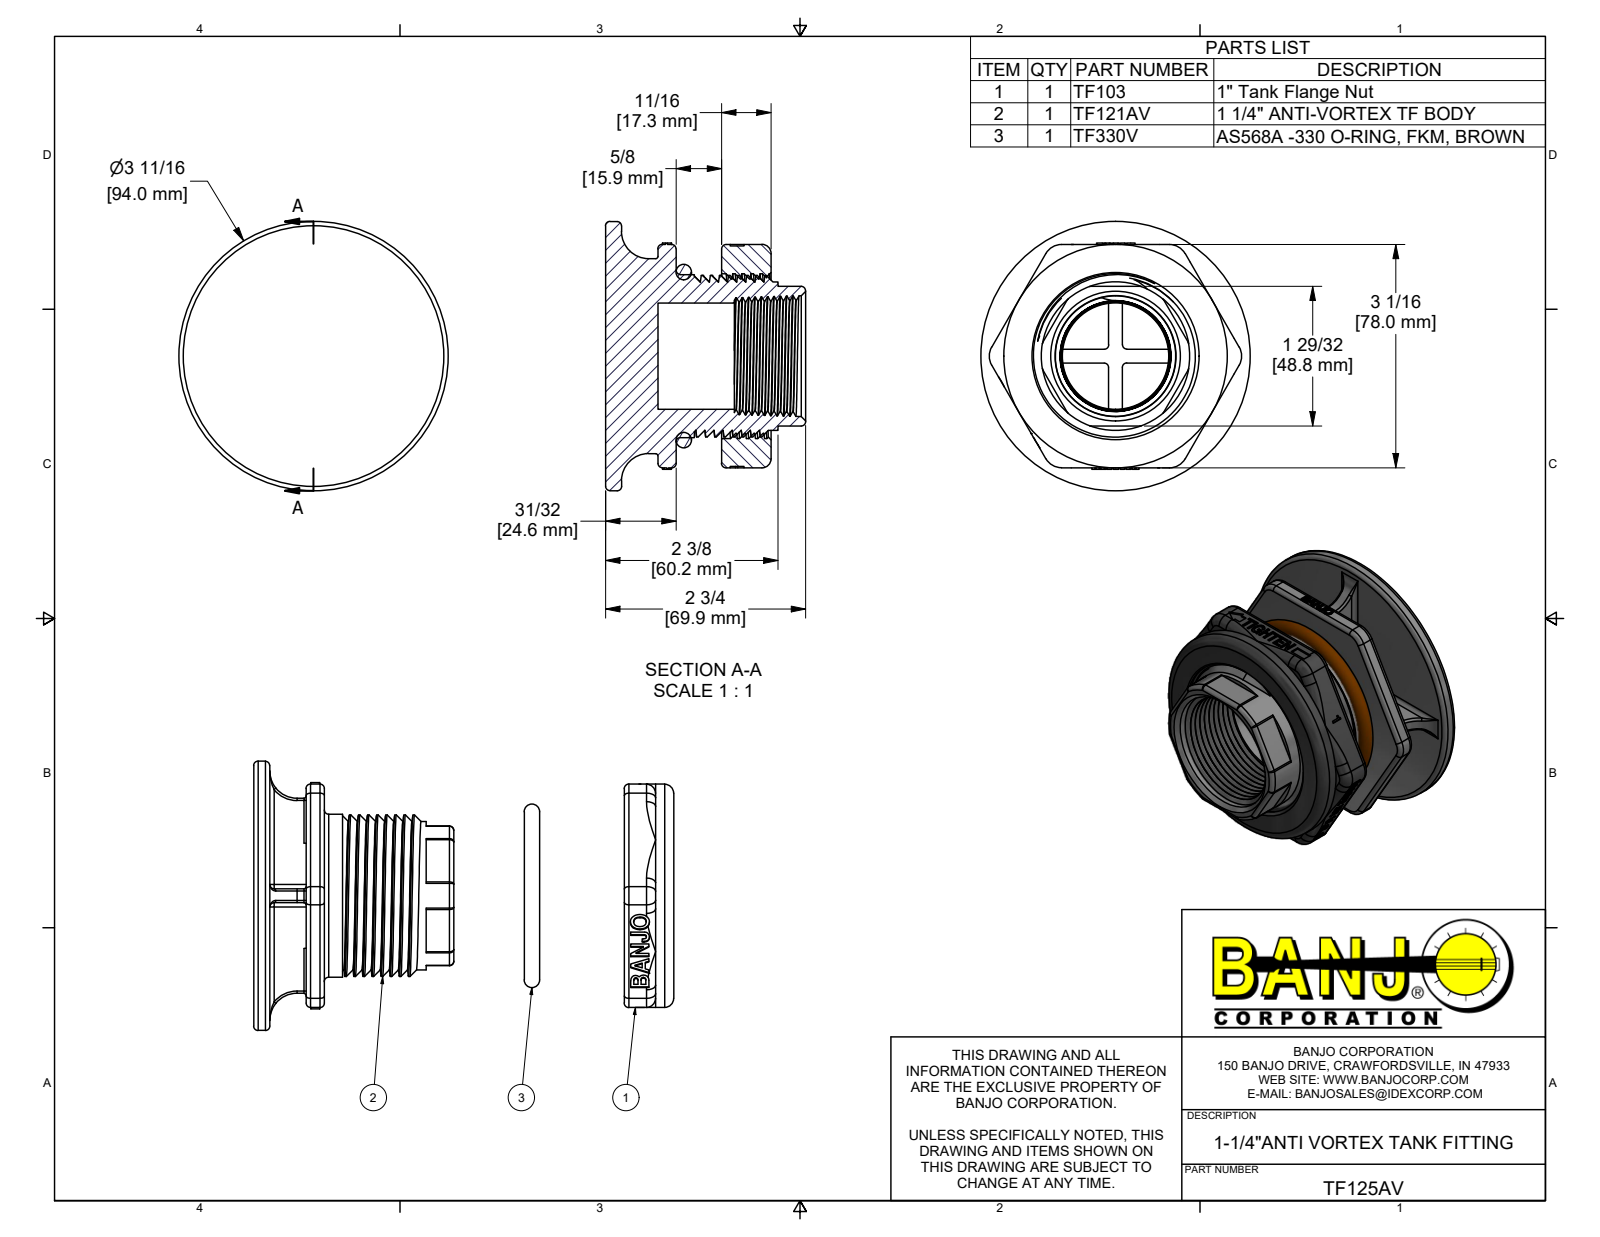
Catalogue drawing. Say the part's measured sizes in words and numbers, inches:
The part is named "TF125AV; TF121AV; TF103; TF103X (+1 more)". Its 3-D file was written by "Autodesk Inventor 2019 (AUTOMOTIVE_DESIGN)". It is 3 solids with 864 faces: 488 planar, 132 cylindrical and 244 other. Overall it measures 26.768 by 3.7 by 3.7 inches. Its volume is 10.37 cubic inches and its surface area 364.3 square inches. Round holes: 1 of diameter 1.46, 1 of diameter 2.12, 1 of diameter 2.265. Round bosses or shafts: 1 of diameter 3.7, 1 of diameter 3.07, 1 of diameter 2.24, 1 of diameter 2.22, 1 of diameter 2.04. Partial cylindrical surfaces (rounded edges, fillets, slot ends): 38 of radius 0.06, 16 of radius 0.03, 6 of radius 0.062, 6 of radius 0.125, 6 of radius 0.25, 4 of radius 0.375, 1 of radius 0.479, 1 of radius 0.6. The main face-to-face distances are 0.22, 0.5, 0.72, 0.25, 1.595, 1.375, 0.875, 0.97, 0.75, 0.625.
